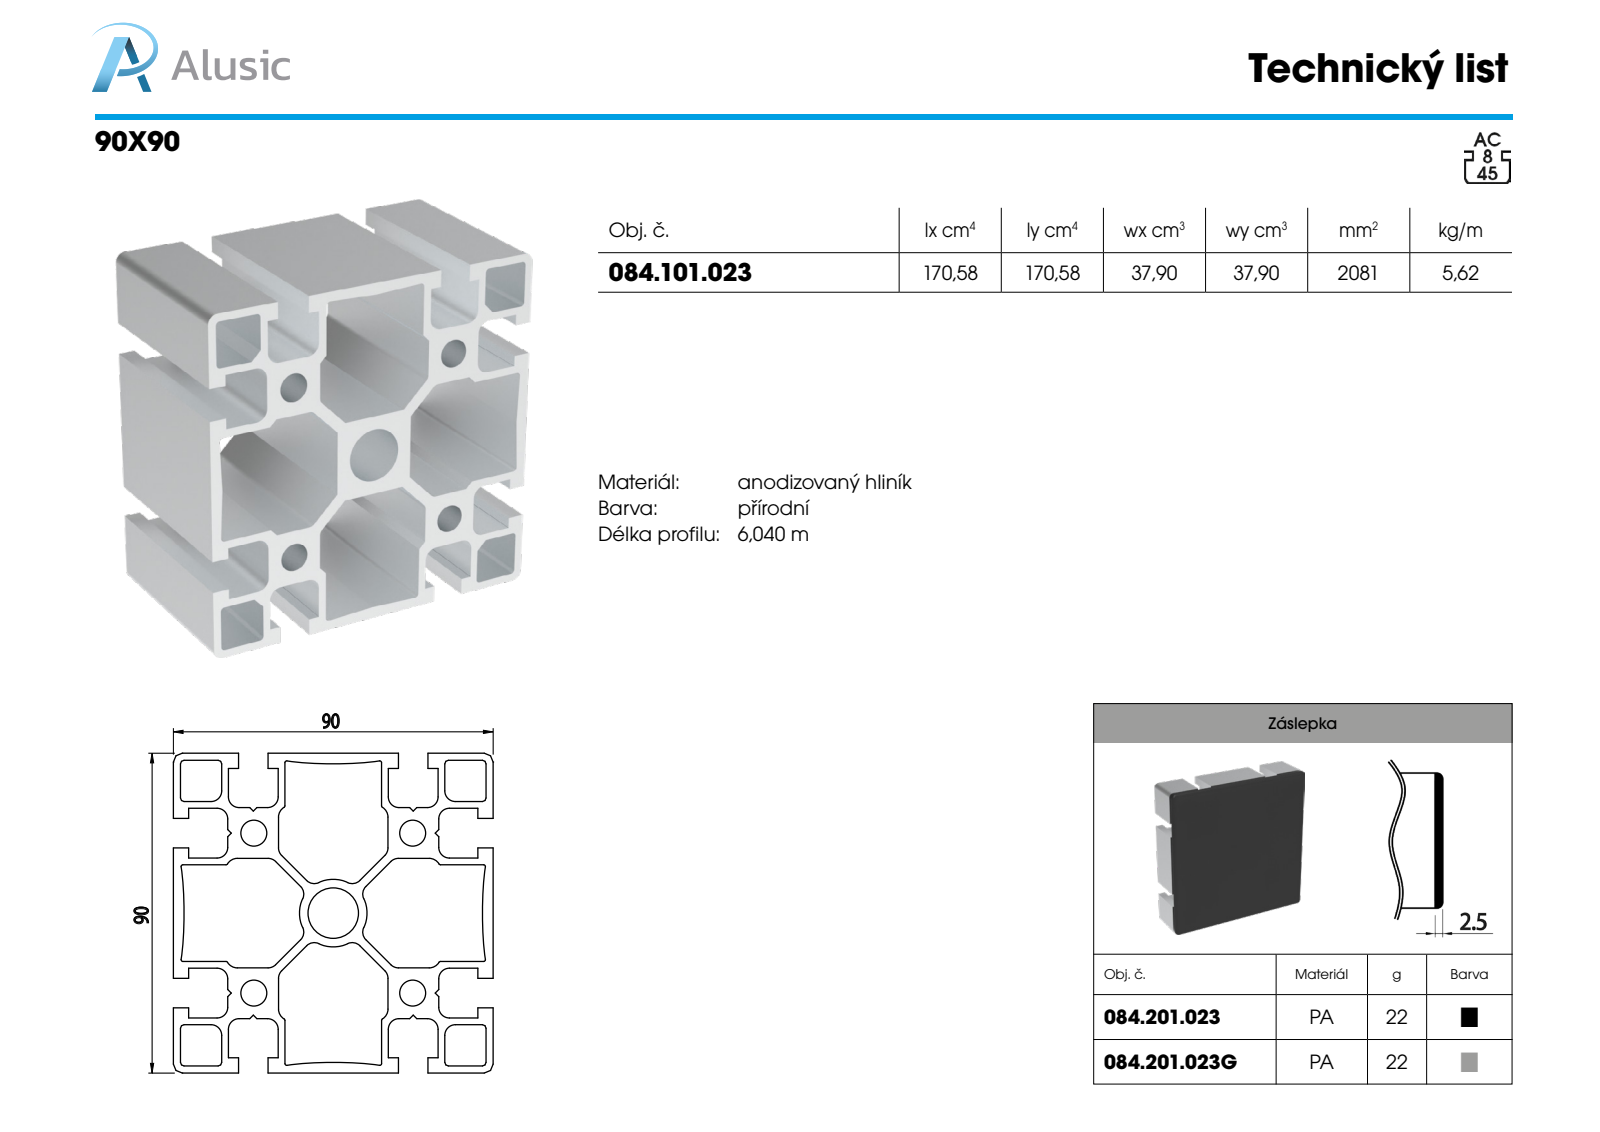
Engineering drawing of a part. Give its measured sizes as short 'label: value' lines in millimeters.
name: 084.101.023
written by: SolidWorks 2018 (AUTOMOTIVE_DESIGN)
unit: mm
bodies: 1 solid, 194 faces (134 planar, 60 cylindrical, 0 other)
size: 100 × 90 × 90
volume: 226 281 mm³; area: 148 181 mm²
holes: 4× ⌀7.3, 1× ⌀13.8
rounds: 20× R1, 16× R3, 8× R2, 4× R2.5
face distances: 90, 58.6, 14.1, 45, 2, 29.4, 88, 29.7, 60.3, 27.7
hole spacings: 31.82, 45, 63.64
